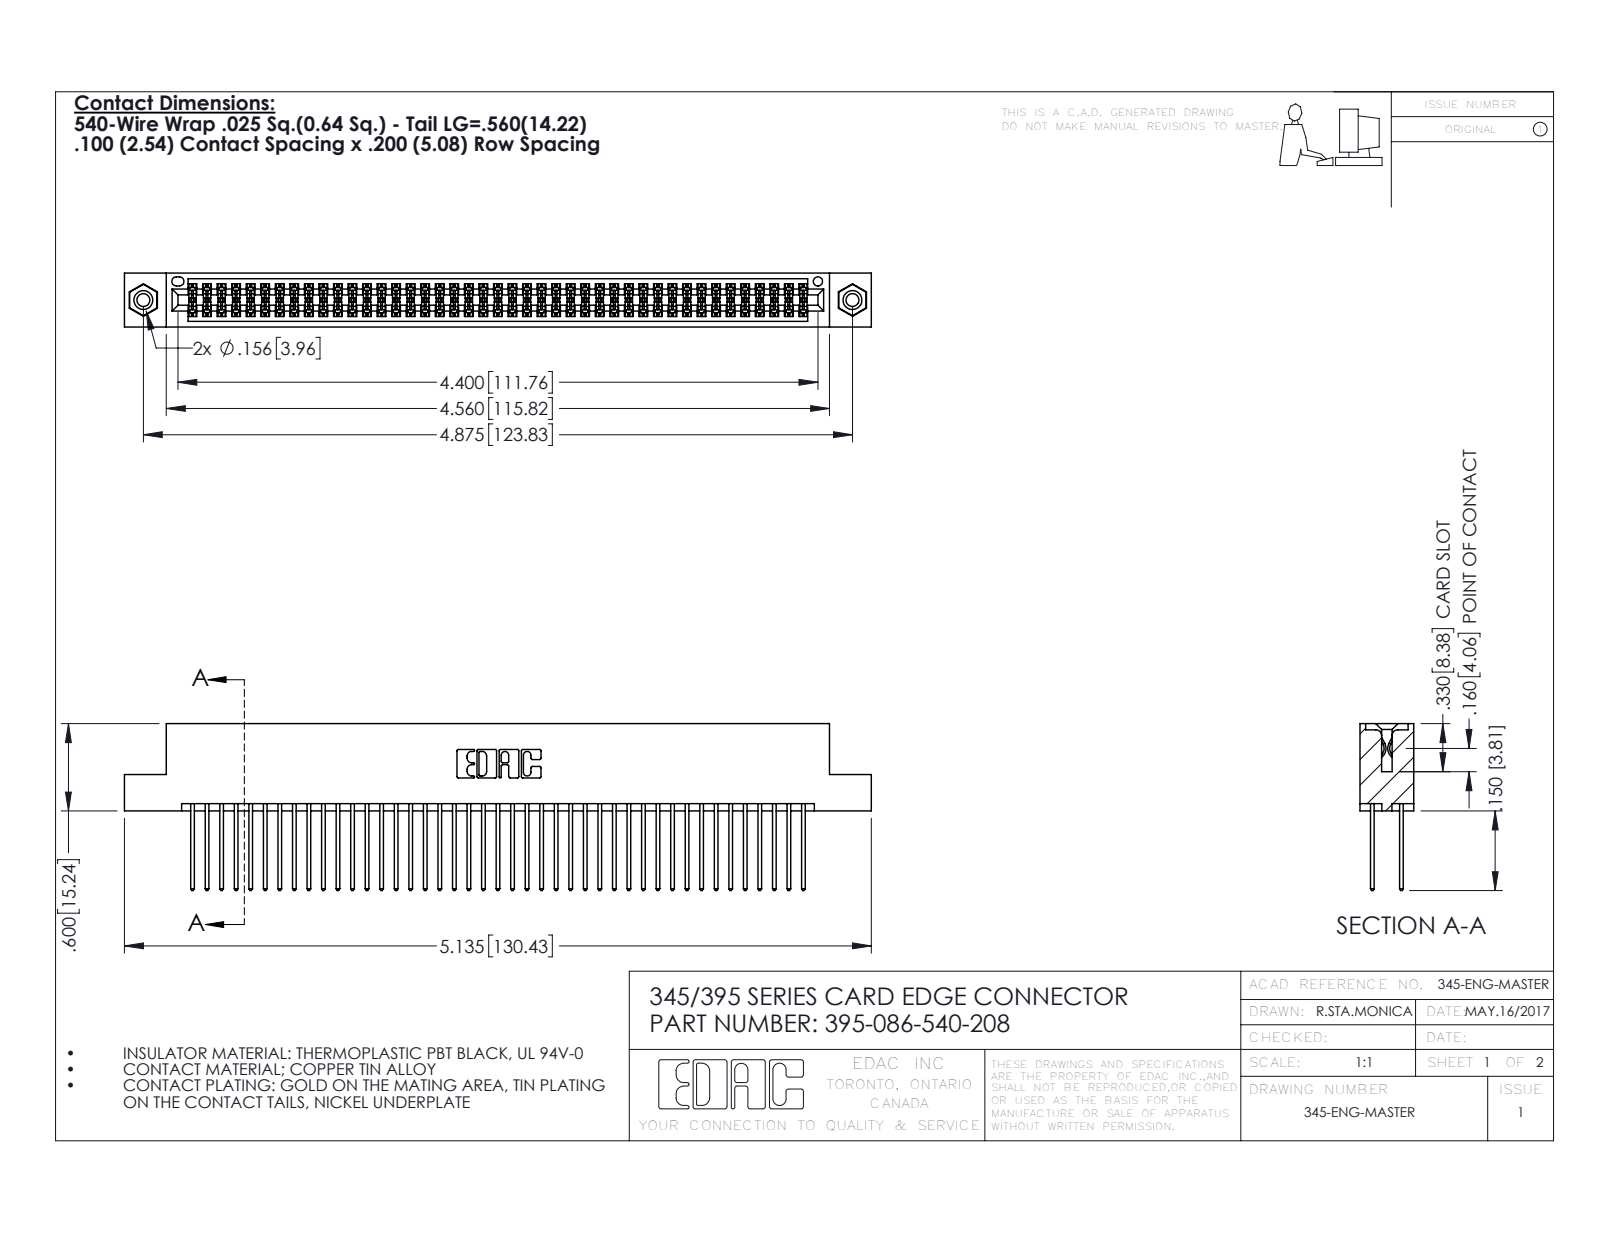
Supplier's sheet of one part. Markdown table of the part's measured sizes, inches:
| quantity | value |
| --- | --- |
| part name | 345-292-001_345-293-140; 395-086-540-208; 345-250-001_345-250-003-102; 345 Part_Flush Mounting Lugs - 0.156 Dia-TI |
| STEP written by | SolidWorks 2016 (CONFIG_CONTROL_DESIGN) |
| units | inches |
| bodies | 89 solids, 4486 faces (2950 planar, 1520 cylindrical, 16 other) |
| overall size | 5.135 × 1.147 × 0.37 |
| volume | 0.793 in³ |
| surface area | 32.18 in² |
| round holes (diameter × count) | 0.089 × 2, 0.125 × 2, 0.156 × 2, 0.064 × 1 |
| round bosses / shafts (diameter × count) | 0.155 × 2 |
| partial cylindrical surfaces (radius × count) | 0.006 × 129, 0.01 × 86, 0.01 × 22, 0.007 × 6, 0.031 × 6, 0.026 × 3, 0.014 × 2, 0.019 × 2 |
| main face-to-face distances | 0.072, 0.298, 0.2, 0.098, 0.272, 0.025, 0.37, 0.225, 0.175, 0.149 |
| hole center spacings | 0.27, 4.639, 4.875 |
